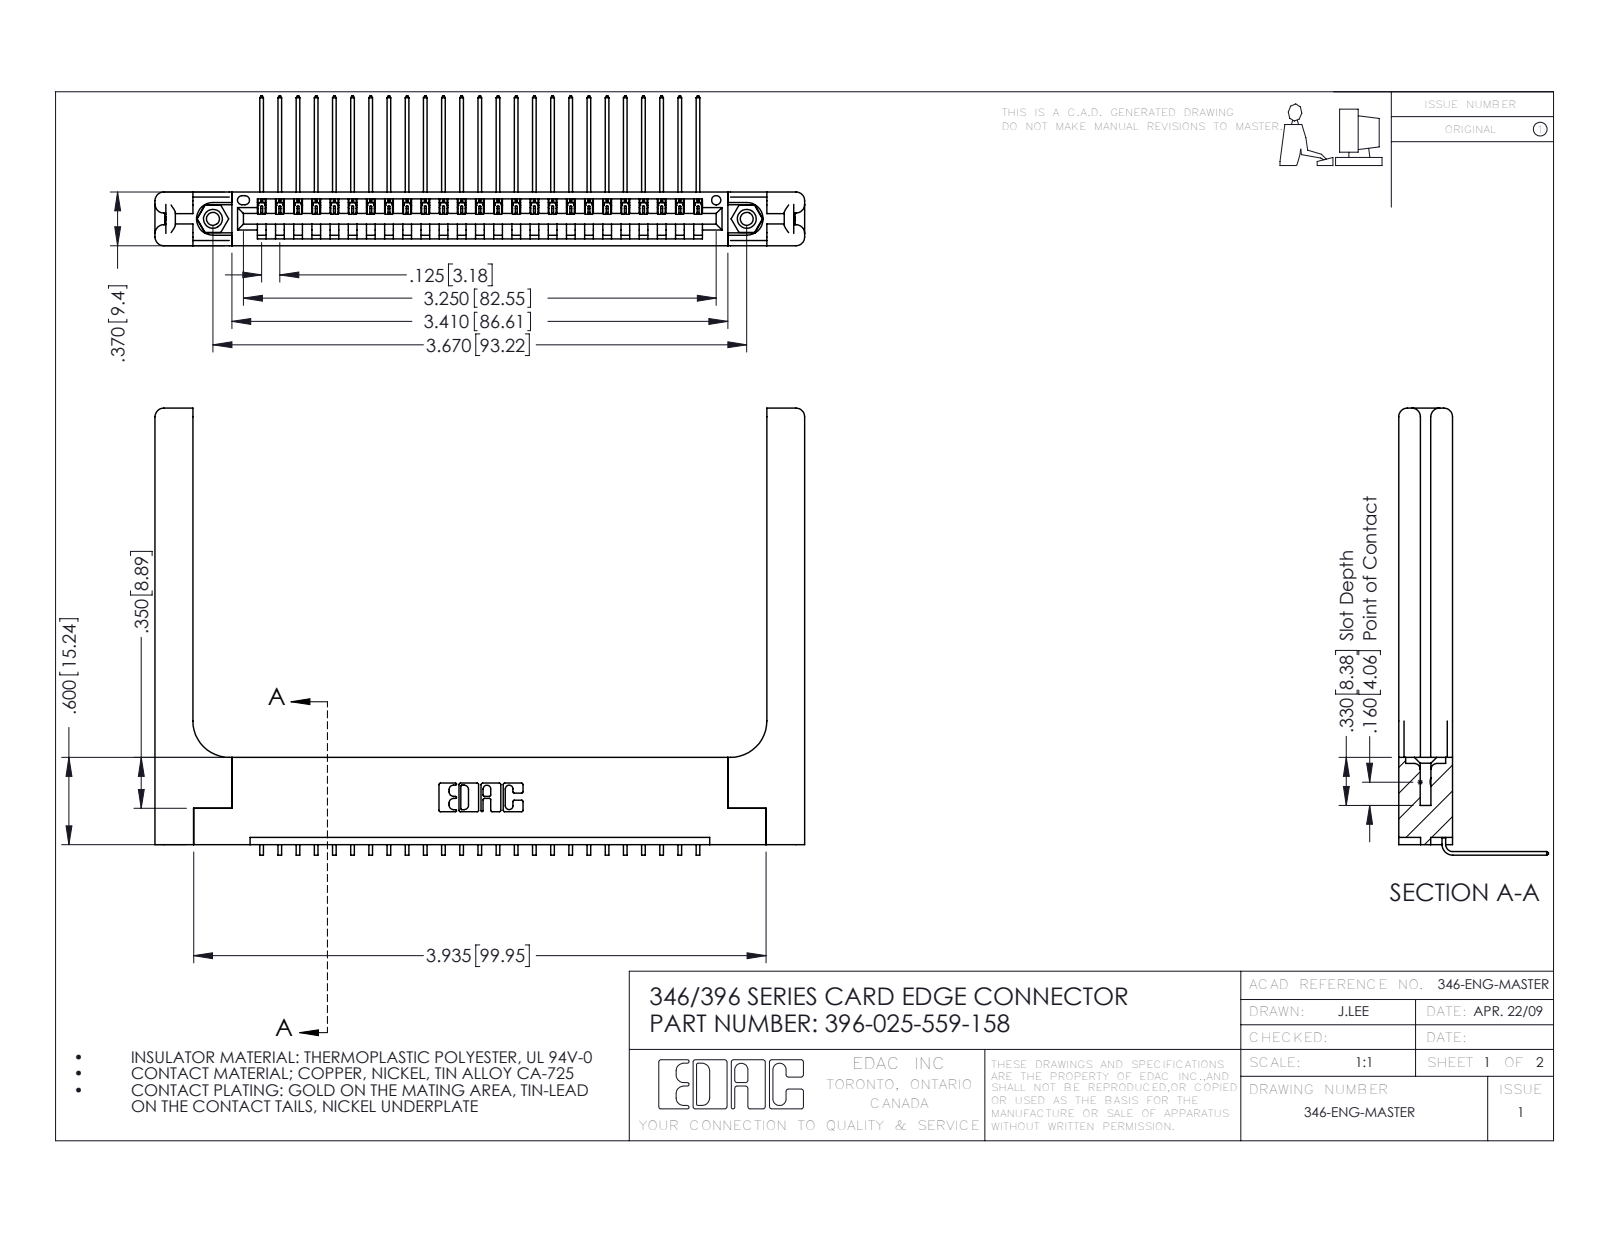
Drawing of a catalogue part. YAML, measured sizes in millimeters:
part_name: "345-250-001_345-250-001-102; 396-025-559-158; 346 Part_Flush Mounting Lugs - 0.156 Dia-TH; 345-292-001_558 559 Tail - 1 (+1 more)"
step_written_by: "SolidWorks 2016 (CONFIG_CONTROL_DESIGN)"
units: millimeters
bodies: {solids: 30, faces: 1878, planar: 1274, cylindrical: 544, other: 60}
overall_size: [113.4, 78.1, 26.2]
volume: 18340
surface_area: 19010
round_holes:
  - {diameter: 2.3, count: 2}
  - {diameter: 3.2, count: 2}
  - {diameter: 4, count: 2}
  - {diameter: 1.6, count: 1}
round_bosses_or_shafts:
  - {diameter: 3.9, count: 2}
partial_cylinders:
  - {radius: 0.2, count: 50}
  - {radius: 0.3, count: 22}
  - {radius: 1.5, count: 16}
  - {radius: 0.2, count: 6}
  - {radius: 0.8, count: 6}
  - {radius: 0.7, count: 3}
  - {radius: 0.8, count: 2}
  - {radius: 0.8, count: 2}
face_to_face_distances: [9.4, 1.8, 1.2, 8.2, 3.8, 3.8, 6.4, 0.6, 7.6, 2]
hole_center_spacings: [6.2, 87.9, 93.2]
